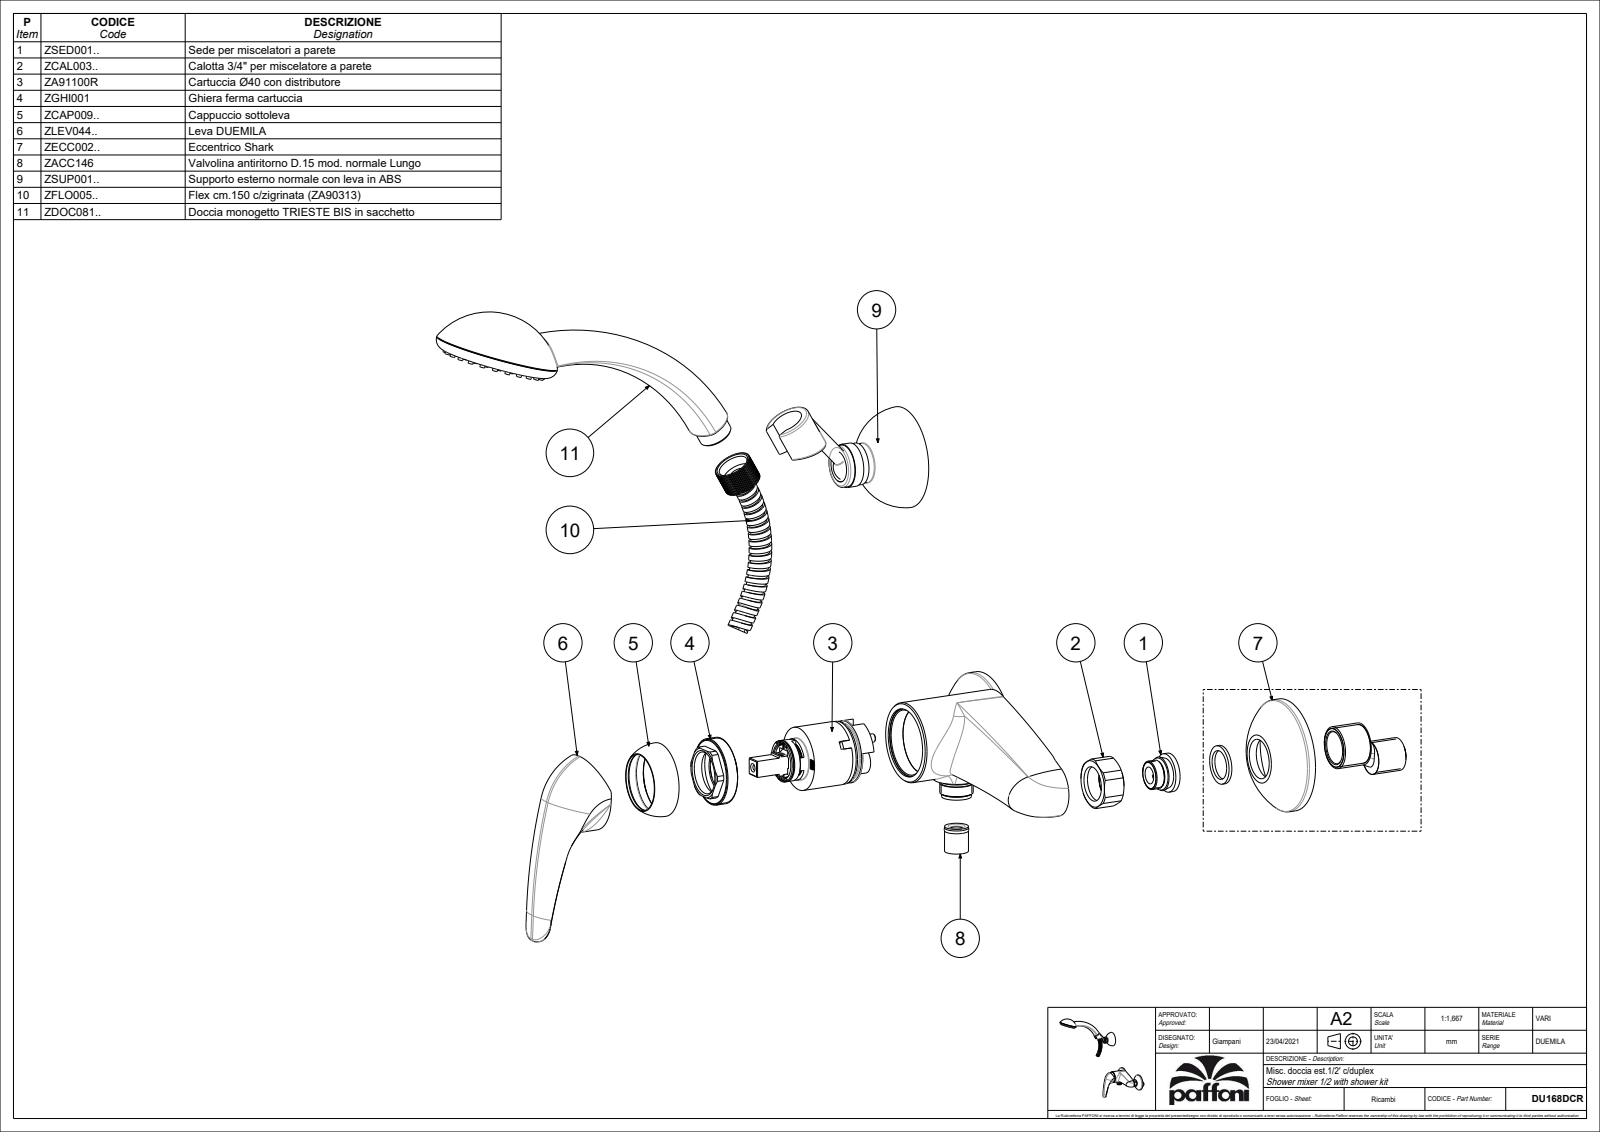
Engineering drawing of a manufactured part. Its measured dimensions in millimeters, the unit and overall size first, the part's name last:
Units: millimetres
Overall size (bounding box): 373.68 × 325.07 × 264.67
Round holes (diameter × count): ⌀8 ×4, ⌀18 ×3, ⌀6 ×2, ⌀7 ×2, ⌀10.5 ×2, ⌀12 ×2, ⌀15 ×2, ⌀16.5 ×2, ⌀19 ×2, ⌀21 ×2, ⌀21.5 ×2, ⌀24.1 ×2
Round bosses / shafts (diameter × count): ⌀70 ×2, ⌀27.6 ×2, ⌀24 ×2, ⌀18.5 ×2, ⌀15.9 ×2, ⌀10 ×2, ⌀9.4 ×2, ⌀75.5 ×1
Partial cylindrical surfaces — rounded edges, fillets, slot ends (radius × count): R0.5 ×63, R0.2 ×24, R0.75 ×16, R1.5 ×6, R0.3 ×4, R15.5 ×3, R3.65 ×2, R3.8 ×2
Main face-to-face distances: 3.5, 14, 3, 10.5, 12, 0.5, 15, 11.5, 13.5, 7
Hole centre spacings: 2, 8.6, 9.9, 13.04, 14, 14.14, 14.76, 69.42
Volume: 276 142 mm³ · Surface area: 223 609 mm²
Bodies: 3 solids, 2534 faces (1049 planar, 624 cylindrical, 861 other)
Part name (STEP PRODUCT): DU168DCR
STEP written by: CREO PARAMETRIC BY PTC INC, 2020044 (CONFIG_CONTROL_DESIGN)
